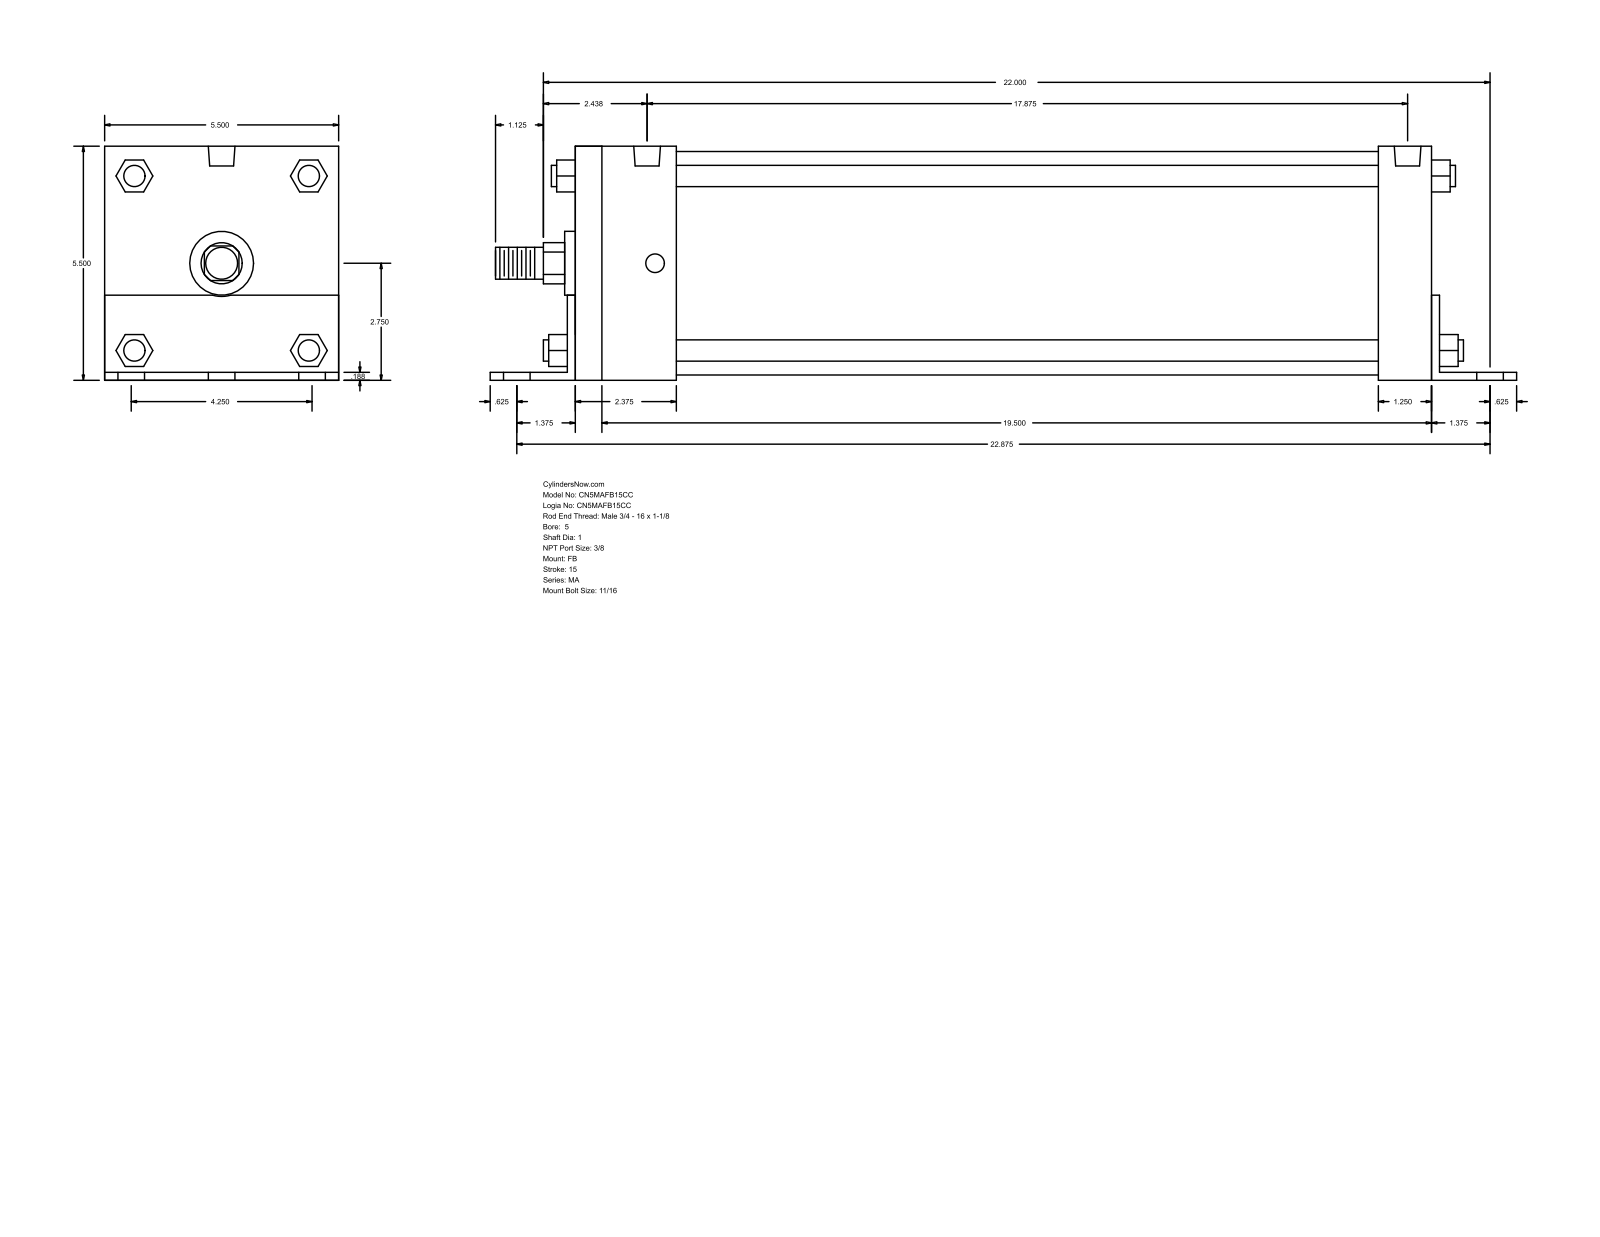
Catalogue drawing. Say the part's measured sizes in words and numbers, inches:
The part is named "MA_FB__0500_1". Its 3-D file was written by "GSSL Pune (CONFIG_CONTROL_DESIGN)". It is 0 solids with 140 faces: 105 planar, 35 cylindrical and 0 other. Overall it measures 24.125 by 5.502 by 5.5 inches. Round holes: 6 of diameter 0.687, 4 of diameter 0.437, 2 of diameter 0.627. Round bosses or shafts: 4 of diameter 0.5, 1 of diameter 5.25, 1 of diameter 1.5, 1 of diameter 1, 1 of diameter 0.75. Partial cylindrical surfaces (rounded edges, fillets, slot ends): 1 of radius 0.484, 1 of radius 0.78. The main face-to-face distances are 5.5, 0.187, 5.502, 20.313, 0.185, 5.315, 20.125, 20.5, 1.437, 1.25. The hole center spacings are 2.125, 22.974, 22.875, 0.187, 2.876, 3.005, 3.728, 3.883.
